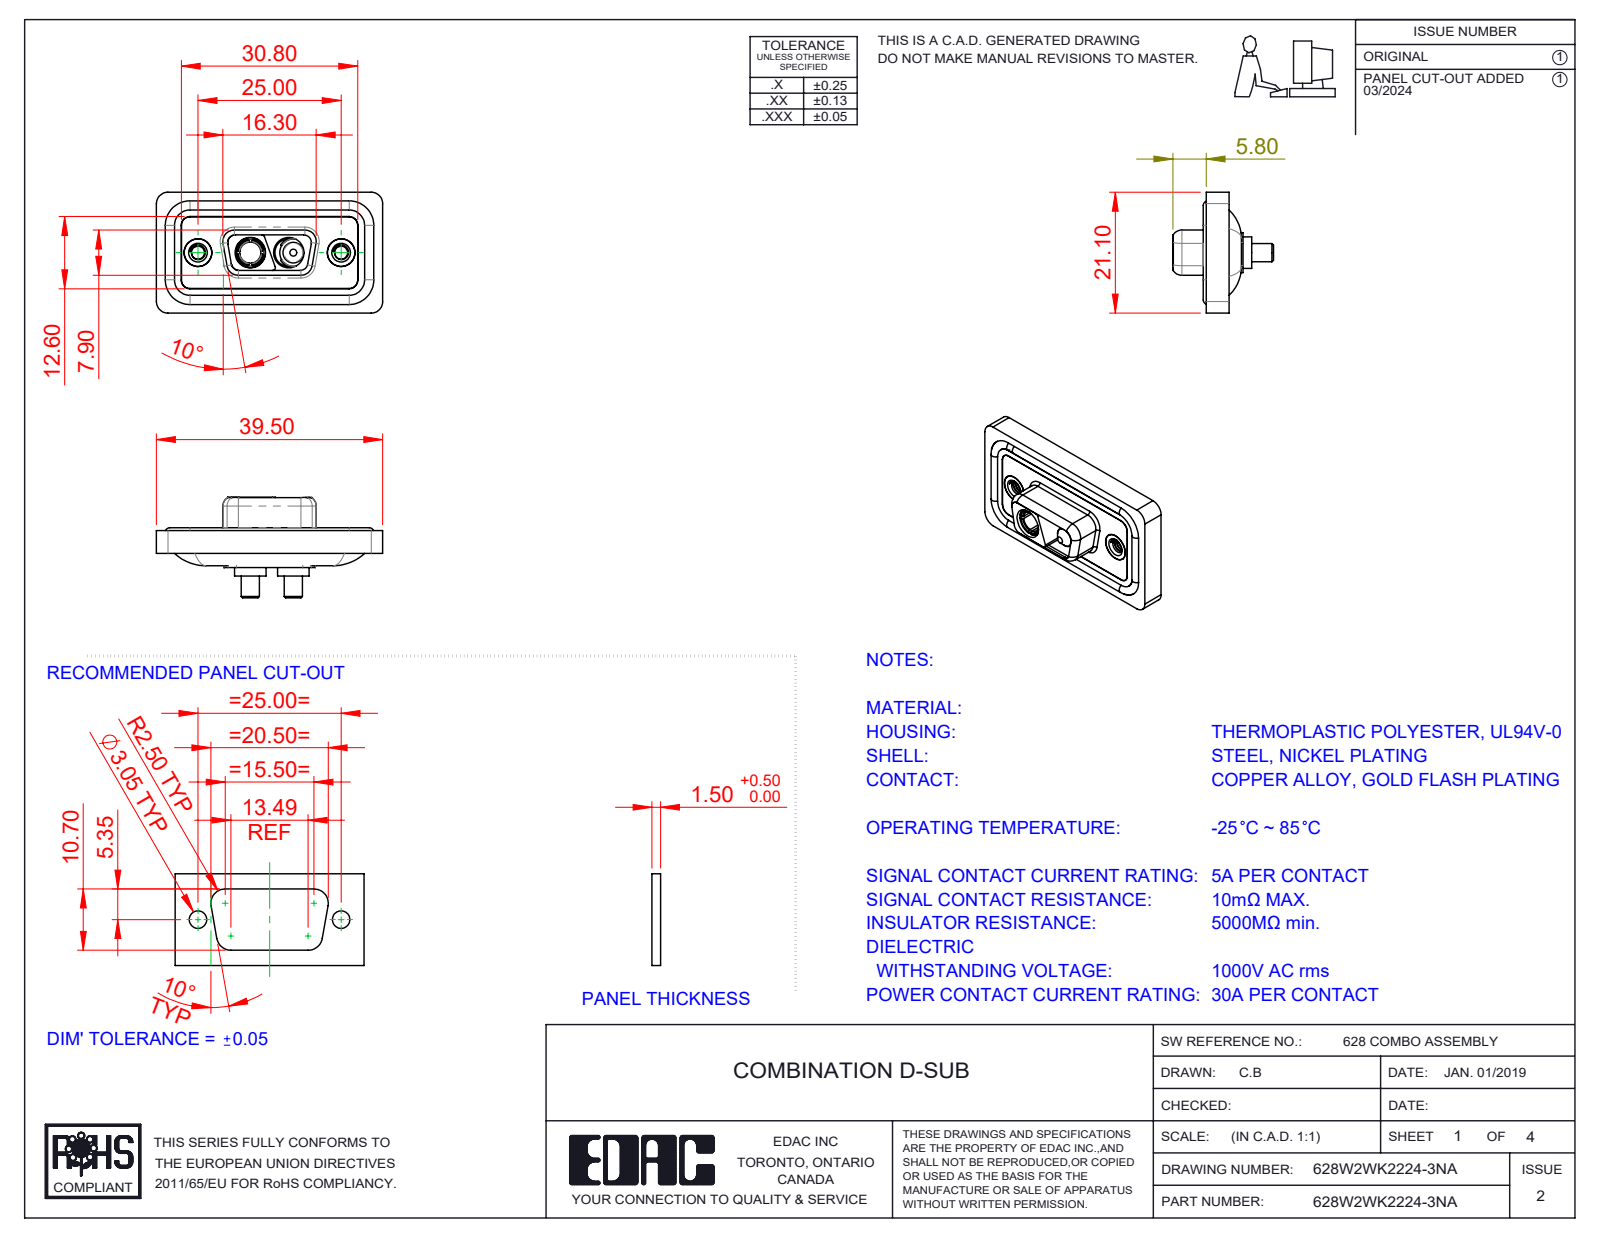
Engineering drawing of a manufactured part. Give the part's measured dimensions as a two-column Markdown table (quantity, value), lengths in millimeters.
| quantity | value |
| --- | --- |
| part name | 628Combo Waterproof Housing_09 Contacts; Power Socket_30A S; 628Combo Shell Rear_09 Contacts; 628Combo Threaded Rivet_A (+4 more) |
| STEP written by | SolidWorks 2023 (CONFIG_CONTROL_DESIGN) |
| units | millimeters |
| bodies | 11 solids, 498 faces (144 planar, 233 cylindrical, 121 other) |
| overall size | 39.5 × 21.1 × 17.55 |
| volume | 4 619 mm³ |
| surface area | 7 350 mm² |
| round holes (diameter × count) | 4.85 × 4, 2.26 × 2, 4 × 2, 4.05 × 2, 5 × 2, 5.3 × 2, 3.7 × 1 |
| round bosses / shafts (diameter × count) | 1.6 × 4, 5.5 × 2, 5.2 × 2, 4.95 × 2, 4.8 × 2, 4.75 × 2, 3.75 × 2, 3.2 × 2 |
| partial cylindrical surfaces (radius × count) | 1.5 × 22, 2 × 18, 1.35 × 8, 1.6 × 8, 0.5 × 6, 0.25 × 4, 0.6 × 4, 0.65 × 4 |
| main face-to-face distances | 0.4, 1.1, 2.9, 1.6, 0.5, 1.8, 5.65, 1.5, 5.35, 3.1 |
| hole center spacings | 9.14, 15.86, 6.72, 25 |
